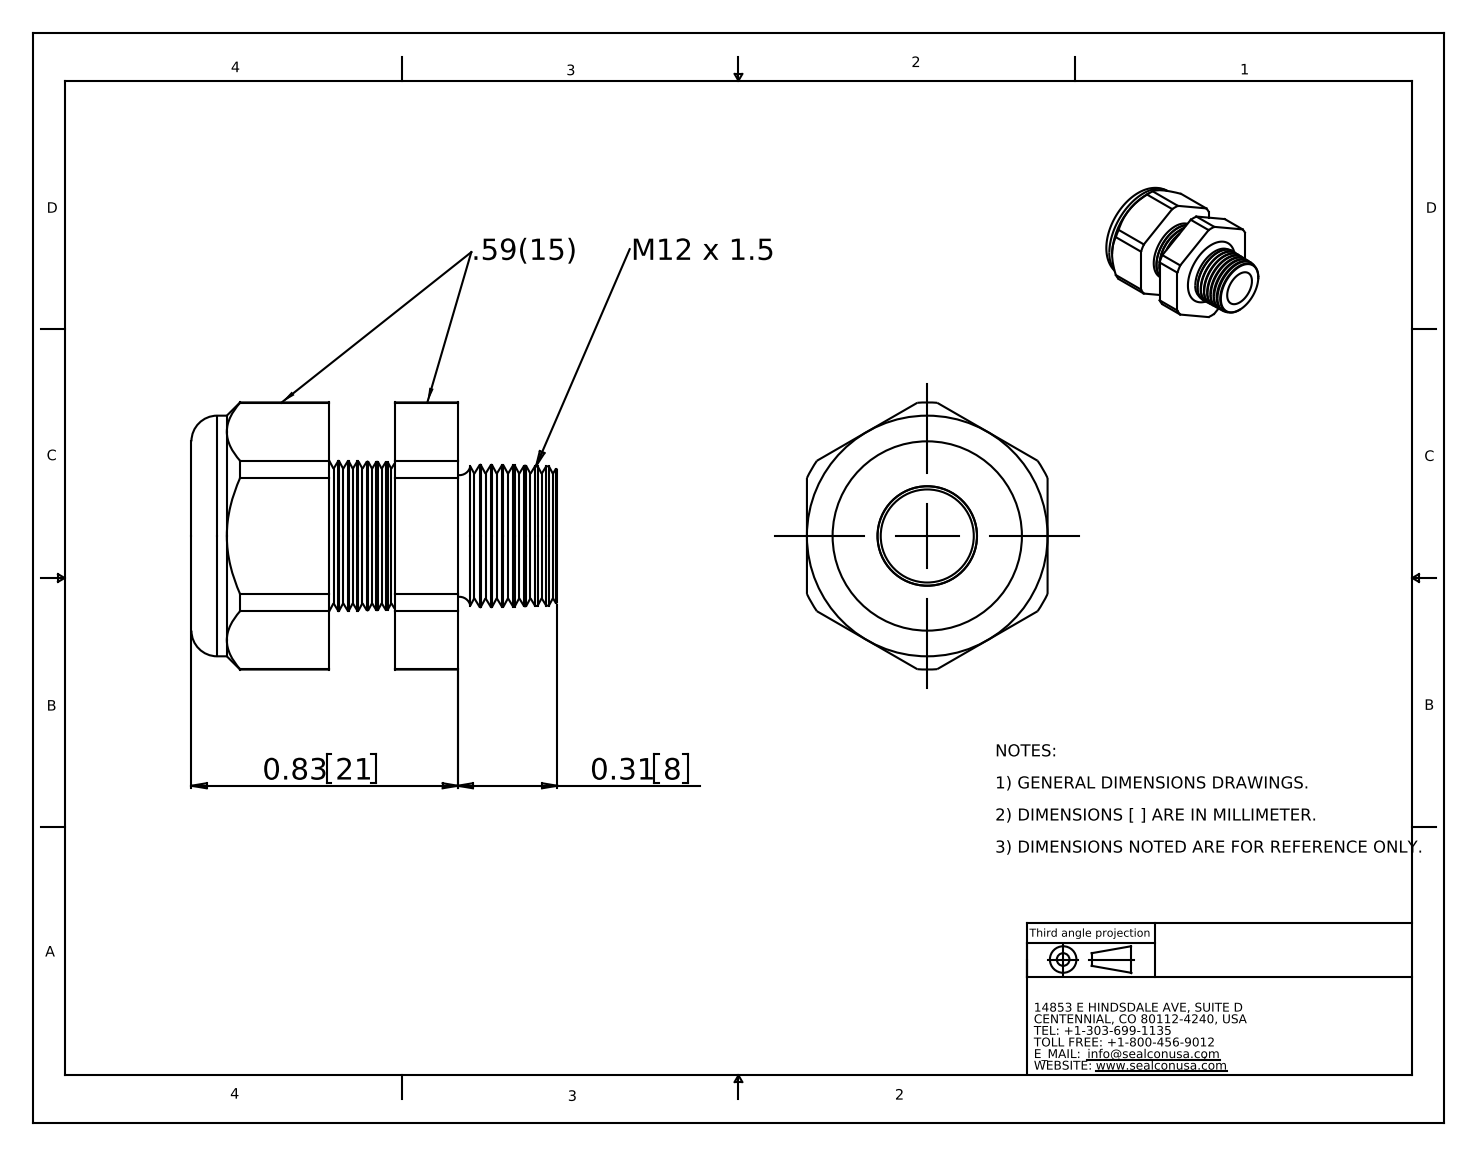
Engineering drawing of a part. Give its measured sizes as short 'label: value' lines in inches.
name: CD12MP-BK
written by: SolidWorks 2007 (CONFIG_CONTROL_DESIGN)
unit: in
bodies: 2 solids, 144 faces (20 planar, 20 cylindrical, 104 other)
size: 1.14 × 0.833 × 0.75
volume: 0.296 in³; area: 5.642 in²
holes: 1× ⌀0.29, 1× ⌀0.31
bosses: 1× ⌀0.75
rounds: 1× R0.416
face distances: 0.75, 0.204, 0.401, 0.197, 0.429, 0.633, 0.83, 0.75, 0.15, 0.279
